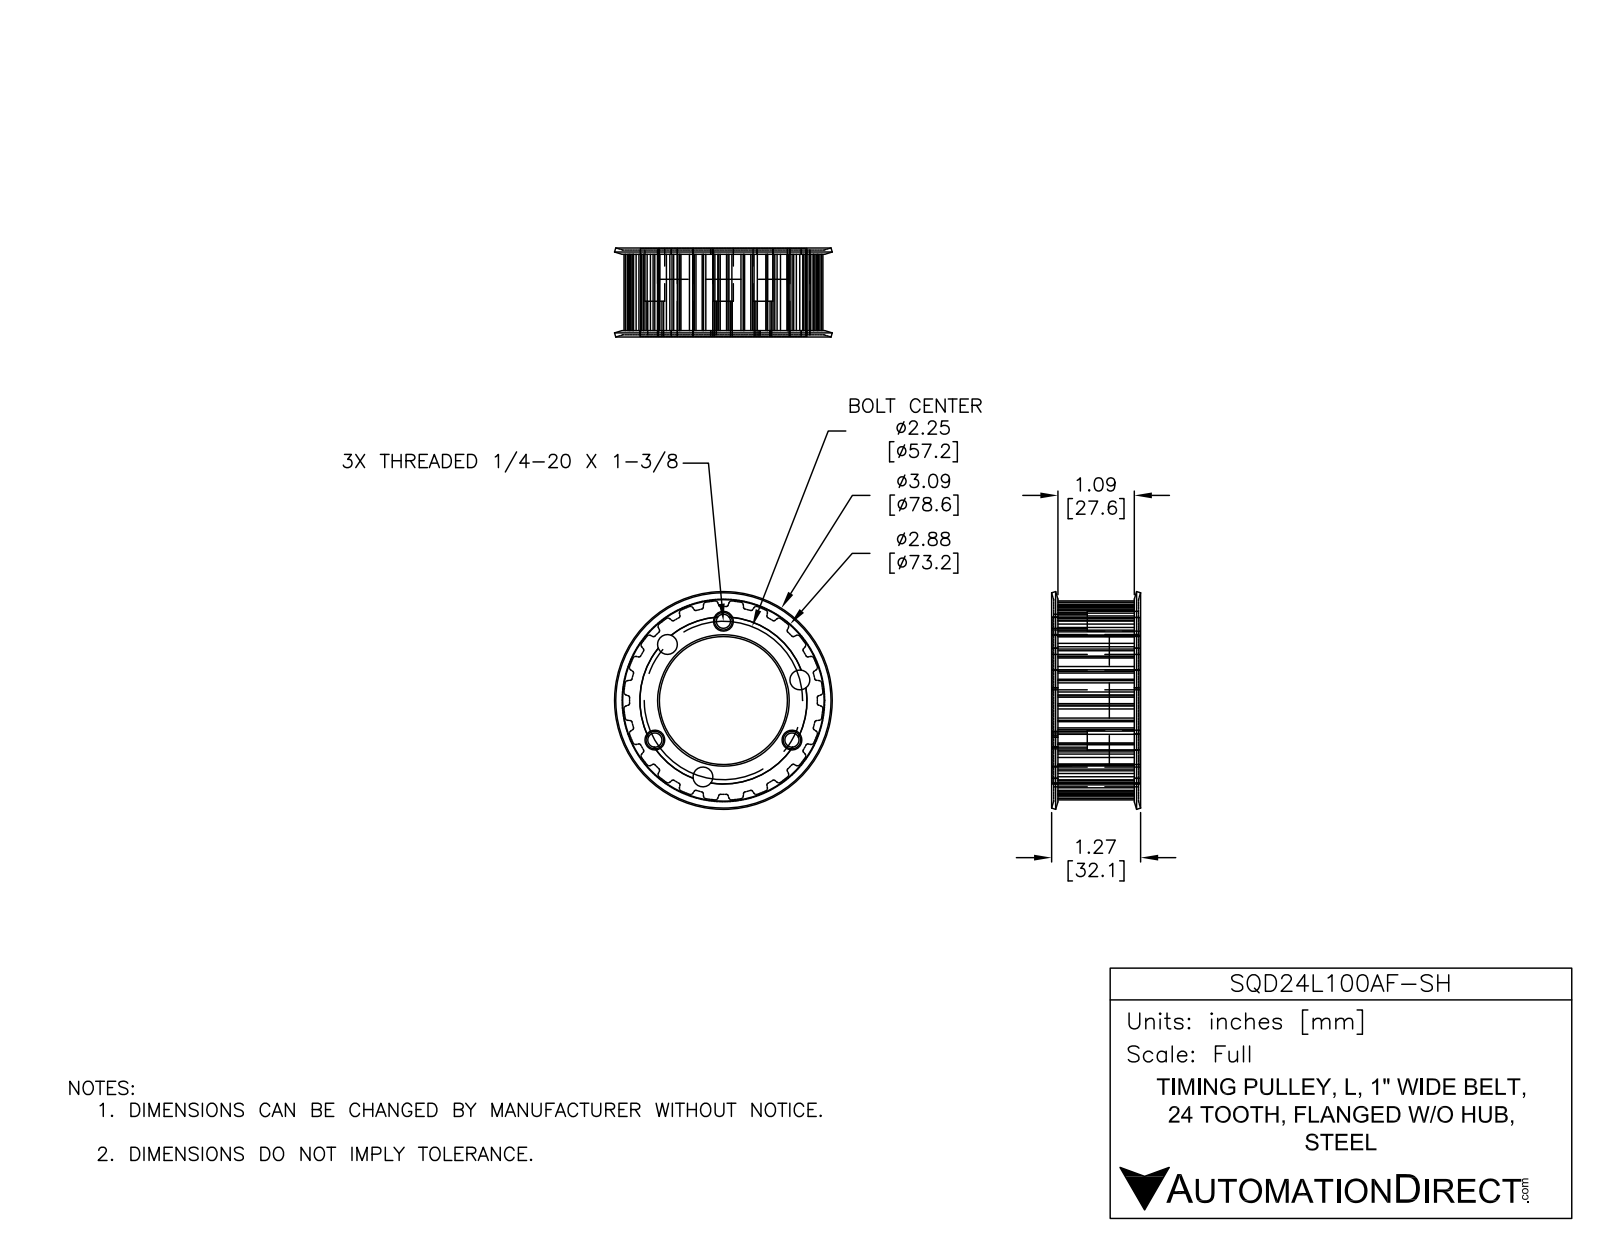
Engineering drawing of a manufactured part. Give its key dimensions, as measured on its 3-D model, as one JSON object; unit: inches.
{"part_name": "SQD24L100AF-SH", "step_written_by": "SolidWorks 2018 (AUTOMOTIVE_DESIGN)", "units": "inches", "bodies": {"solids": 1, "faces": 293, "planar": 93, "cylindrical": 185, "other": 15}, "overall_size": [3.094, 3.094, 1.265], "volume_in3": 3.892, "surface_area_in2": 40.2, "round_holes": [[0.281, 6], [0.201, 3], [1.82, 1]], "round_bosses_or_shafts": [[2.371, 1]], "partial_cylinders_radius": [[0.021, 48], [0.04, 48], [1.187, 1], [1.188, 1], [1.419, 1]], "face_to_face_distances": [0.022, 1.228, 1.205, 1.25, 1.167, 1.145, 0.06, 0.083, 0.082, 0.06], "hole_center_spacings": [1.125, 1.948, 0.861, 1.125, 1.37, 1.949, 2.231, 1.37]}
